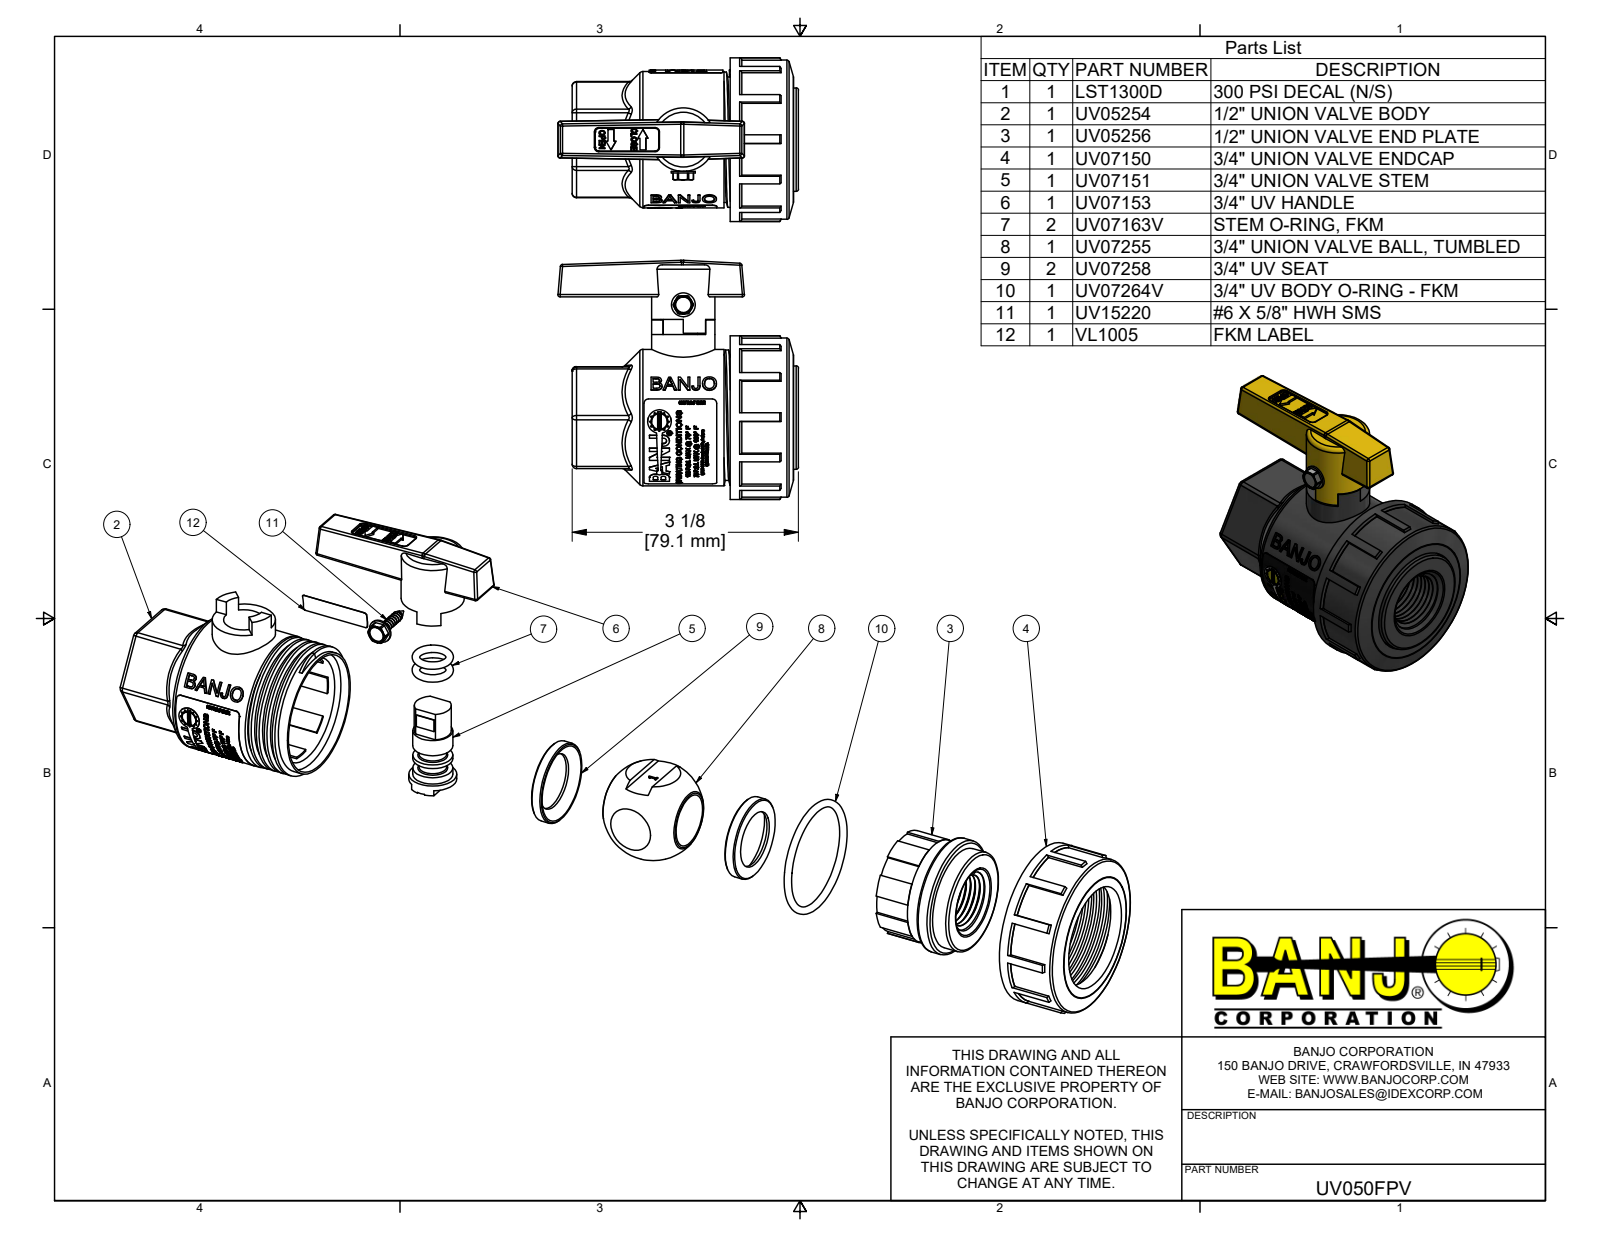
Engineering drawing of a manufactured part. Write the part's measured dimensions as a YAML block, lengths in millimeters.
part_name: "UV050FPV; UV07150; UV07151; UV07255 (+8 more)"
step_written_by: "Autodesk Inventor 2019 (AUTOMOTIVE_DESIGN)"
units: millimeters
bodies: {solids: 14, faces: 2478, planar: 1238, cylindrical: 390, other: 850}
overall_size: [346.3, 83.5, 57.2]
volume: 119100
surface_area: 103400
round_holes:
  - {diameter: 13.1, count: 1}
  - {diameter: 14.2, count: 1}
  - {diameter: 18.5, count: 1}
  - {diameter: 19.1, count: 1}
  - {diameter: 19.3, count: 1}
  - {diameter: 20.1, count: 1}
  - {diameter: 29.3, count: 1}
  - {diameter: 29.4, count: 1}
  - {diameter: 36.8, count: 1}
  - {diameter: 38.1, count: 1}
  - {diameter: 42.4, count: 1}
  - {diameter: 45.2, count: 1}
round_bosses_or_shafts:
  - {diameter: 57.2, count: 1}
  - {diameter: 55.5, count: 1}
  - {diameter: 47.6, count: 1}
  - {diameter: 47.2, count: 1}
  - {diameter: 43.8, count: 1}
  - {diameter: 41.3, count: 1}
  - {diameter: 37.1, count: 1}
  - {diameter: 36.1, count: 1}
partial_cylinders:
  - {radius: 0.8, count: 27}
  - {radius: 1.5, count: 16}
  - {radius: 0.3, count: 4}
  - {radius: 1.3, count: 4}
  - {radius: 12.7, count: 3}
  - {radius: 3.5, count: 1}
  - {radius: 6.5, count: 1}
  - {radius: 6.7, count: 1}
face_to_face_distances: [2.8, 18.6, 49.7, 31.1, 17.8, 35.6, 0.8, 31.9, 24.6, 23.3]
